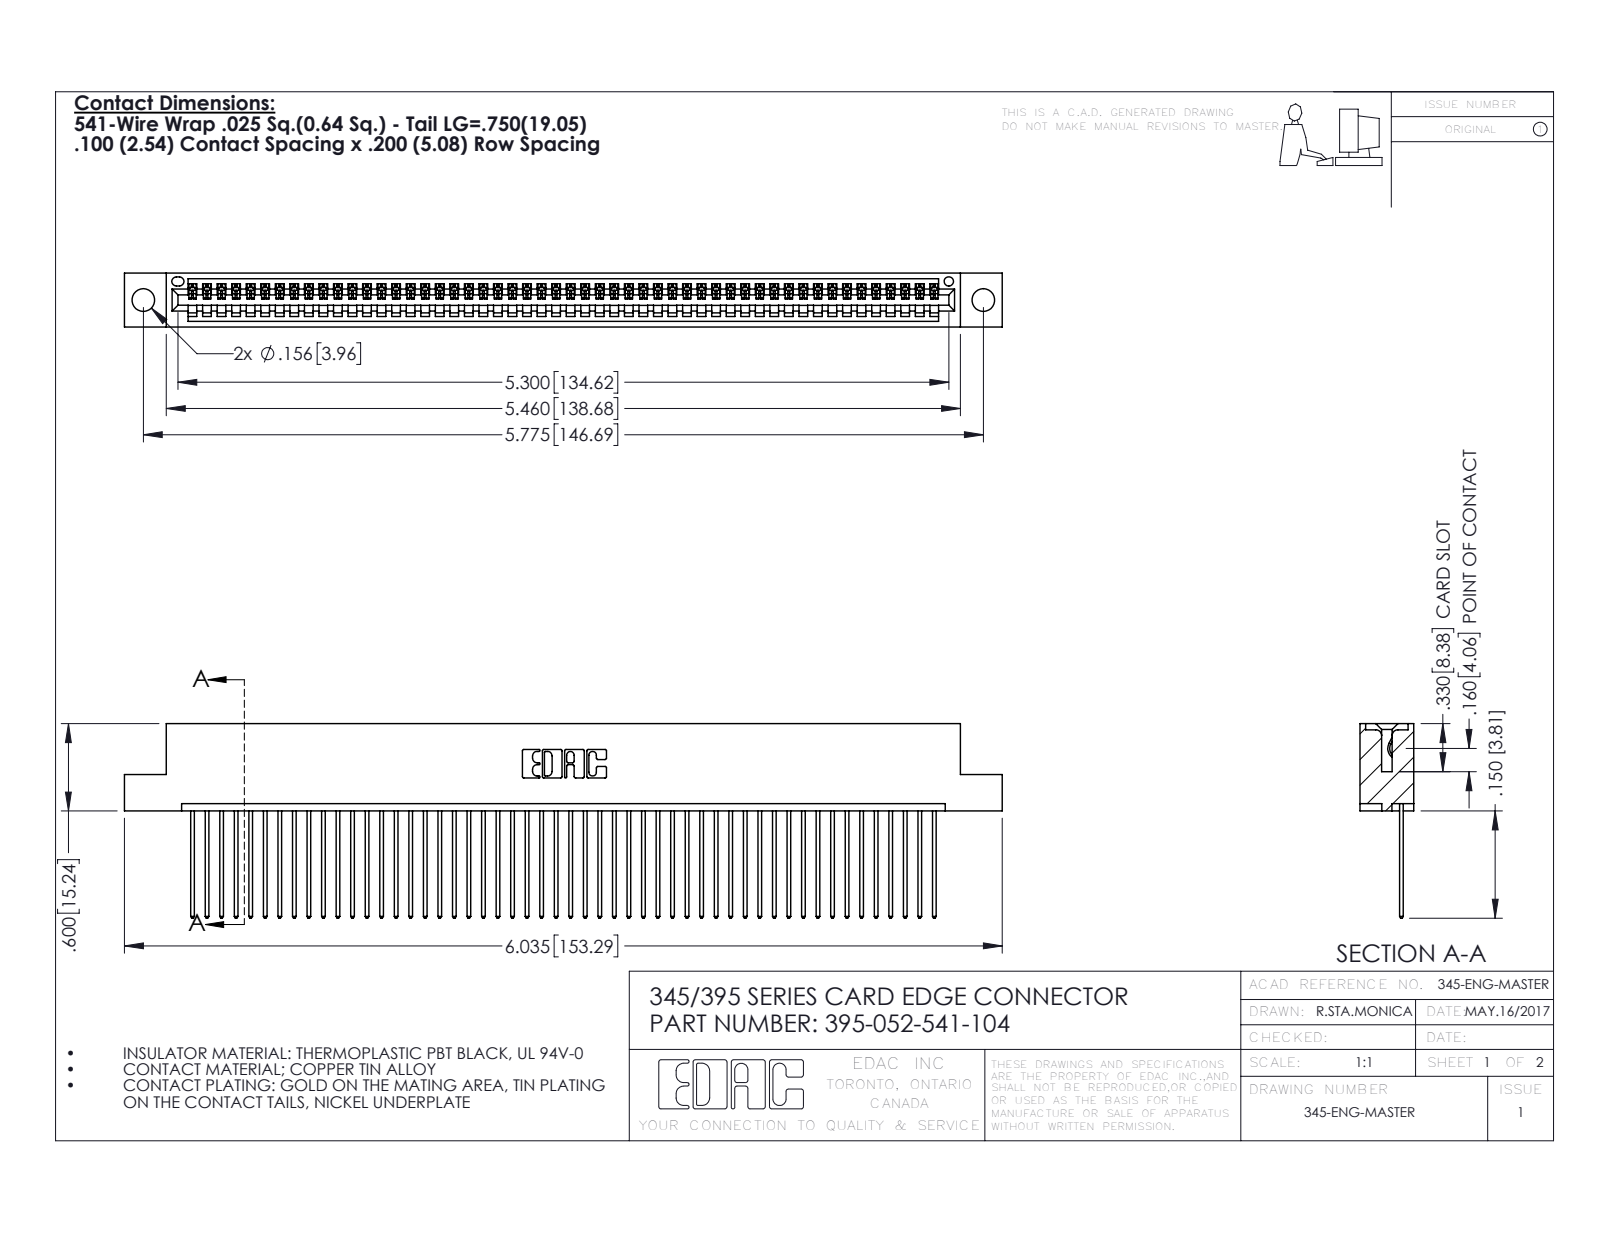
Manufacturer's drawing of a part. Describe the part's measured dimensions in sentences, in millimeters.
The part is named "345-292-001_345-293-141; 345 Part_Flush Mounting Lugs - 0.156 Dia-TH; 395-052-541-104". Its 3-D file was written by "SolidWorks 2016 (CONFIG_CONTROL_DESIGN)". It is 53 solids with 3142 faces: 2160 planar, 982 cylindrical and 0 other. Overall it measures 153.3 by 34 by 9.4 millimeters. Its volume is 14 700 cubic millimeters and its surface area 20 520 square millimeters. Round holes: 2 of diameter 4, 1 of diameter 1.6. Partial cylindrical surfaces (rounded edges, fillets, slot ends): 104 of radius 0.2, 104 of radius 0.3, 22 of radius 0.3, 6 of radius 0.2, 6 of radius 0.8, 3 of radius 0.7, 2 of radius 0.8, 2 of radius 1. The main face-to-face distances are 1.8, 7.6, 2.5, 6.9, 0.6, 9.4, 5.1, 5.7, 3.8, 1.8. The hole center spacings are 6.9, 140.7, 146.7.
